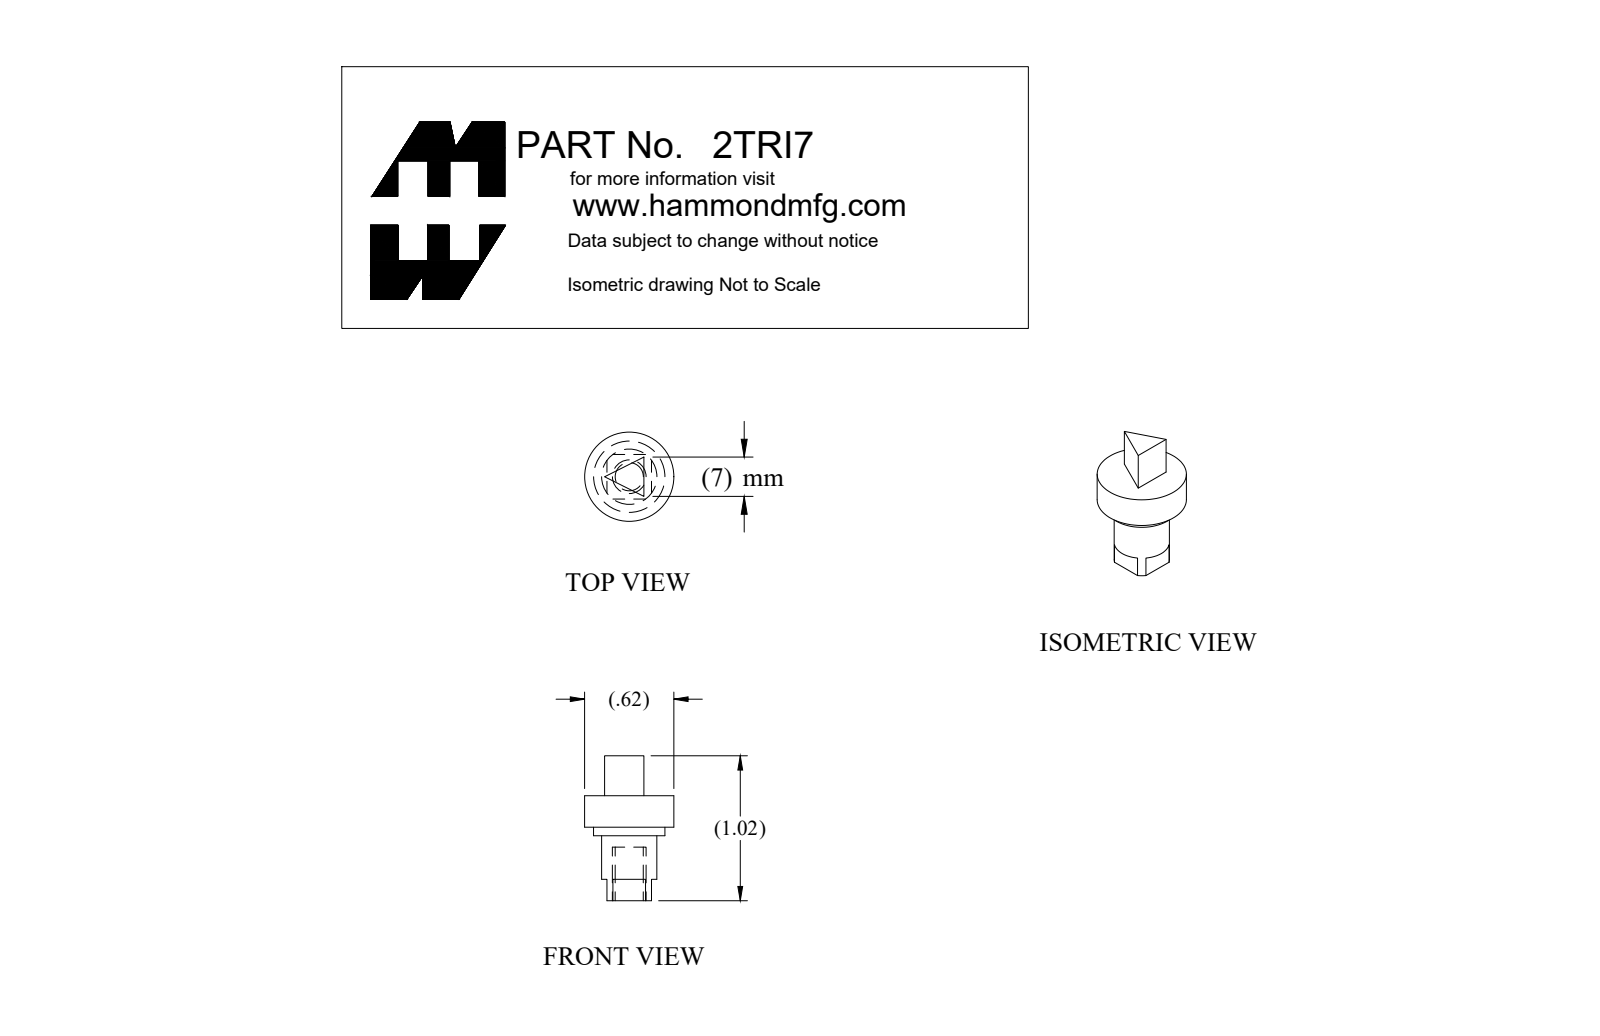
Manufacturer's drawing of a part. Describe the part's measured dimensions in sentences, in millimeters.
The part is named "2TRI7". Its 3-D file was written by "SolidWorks 2018 (AUTOMOTIVE_DESIGN)". It is 1 solid with 21 faces: 17 planar, 4 cylindrical and 0 other. Overall it measures 25.8 by 15.9 by 15.9 millimeters. Its volume is 2 110 cubic millimeters and its surface area 1 397 square millimeters. Round holes: 1 of diameter 5. Round bosses or shafts: 1 of diameter 15.9, 1 of diameter 12.7, 1 of diameter 9.8. The main face-to-face distances are 7.1, 5.6, 1.5, 7.9, 11.6, 13.1, 18.7, 25.8, 14.2, 12.7.
